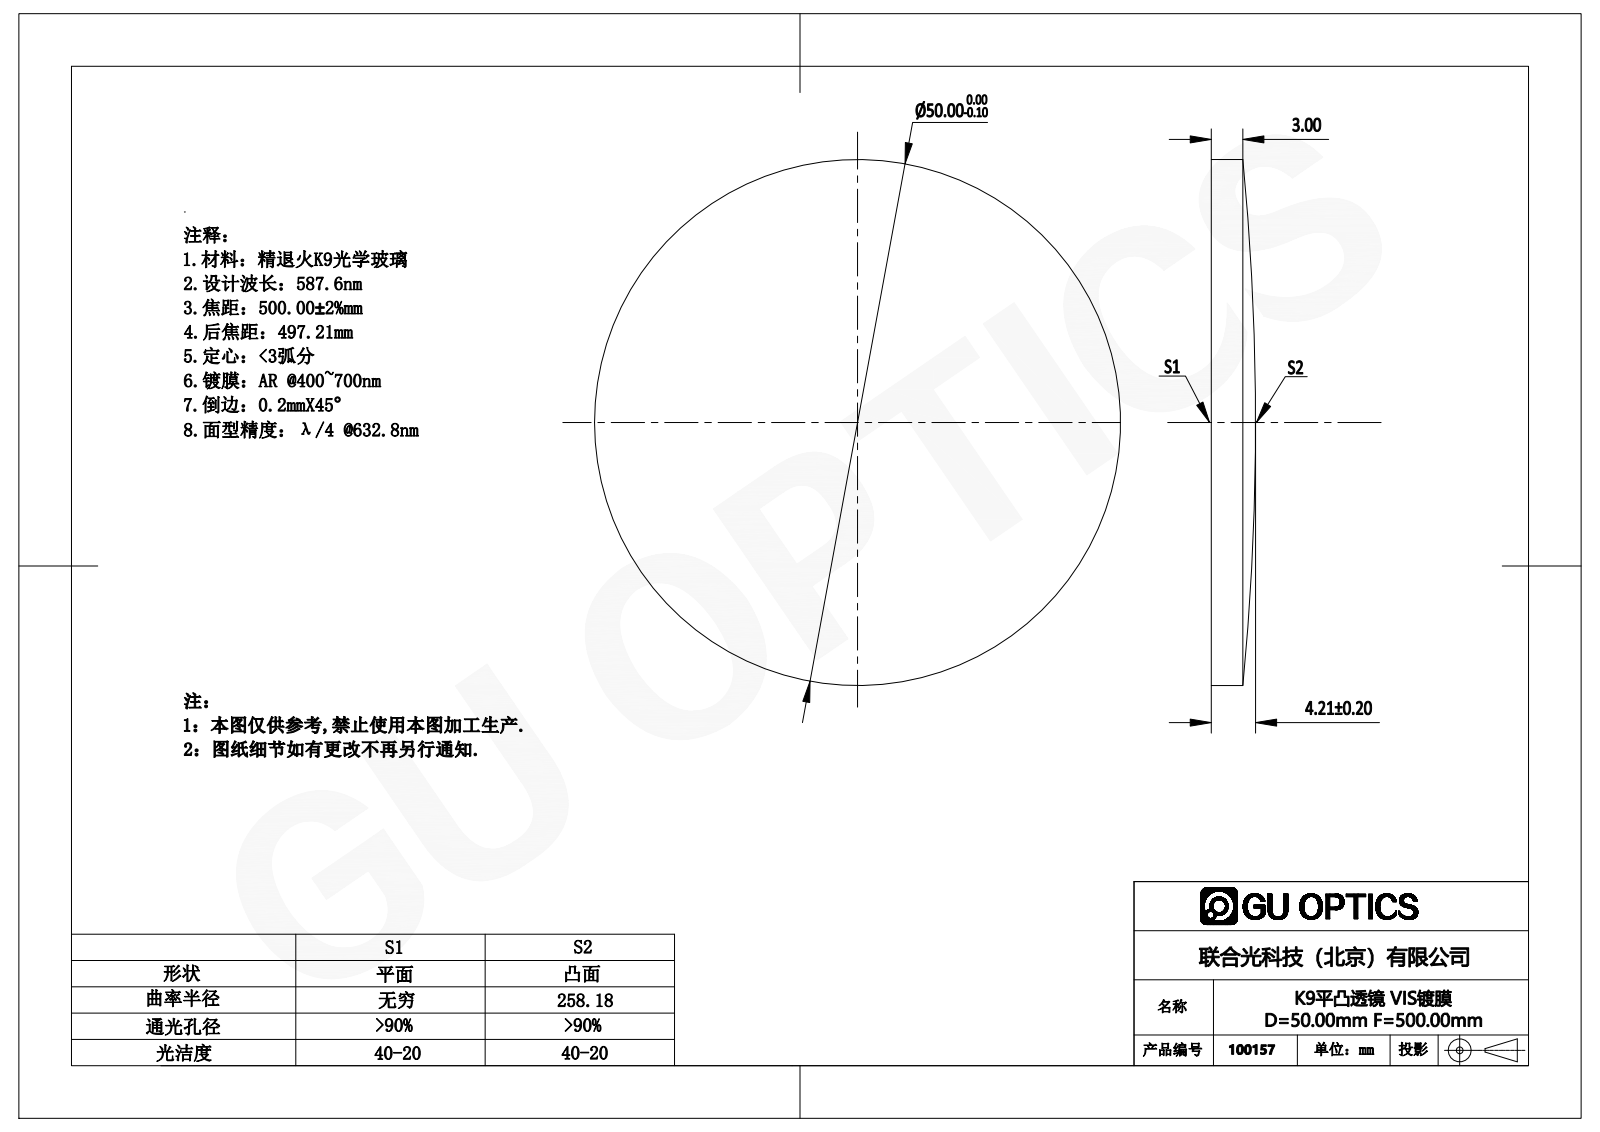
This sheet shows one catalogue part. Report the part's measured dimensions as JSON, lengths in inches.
{"part_name": "100157", "step_written_by": "SolidWorks 2016 (AUTOMOTIVE_DESIGN)", "units": "inches", "bodies": {"solids": 1, "faces": 5, "planar": 1, "cylindrical": 2, "other": 2}, "overall_size": [1.969, 1.969, 0.166], "volume_in3": 0.432, "surface_area_in2": 6.825, "round_bosses_or_shafts": [[1.969, 1]]}
